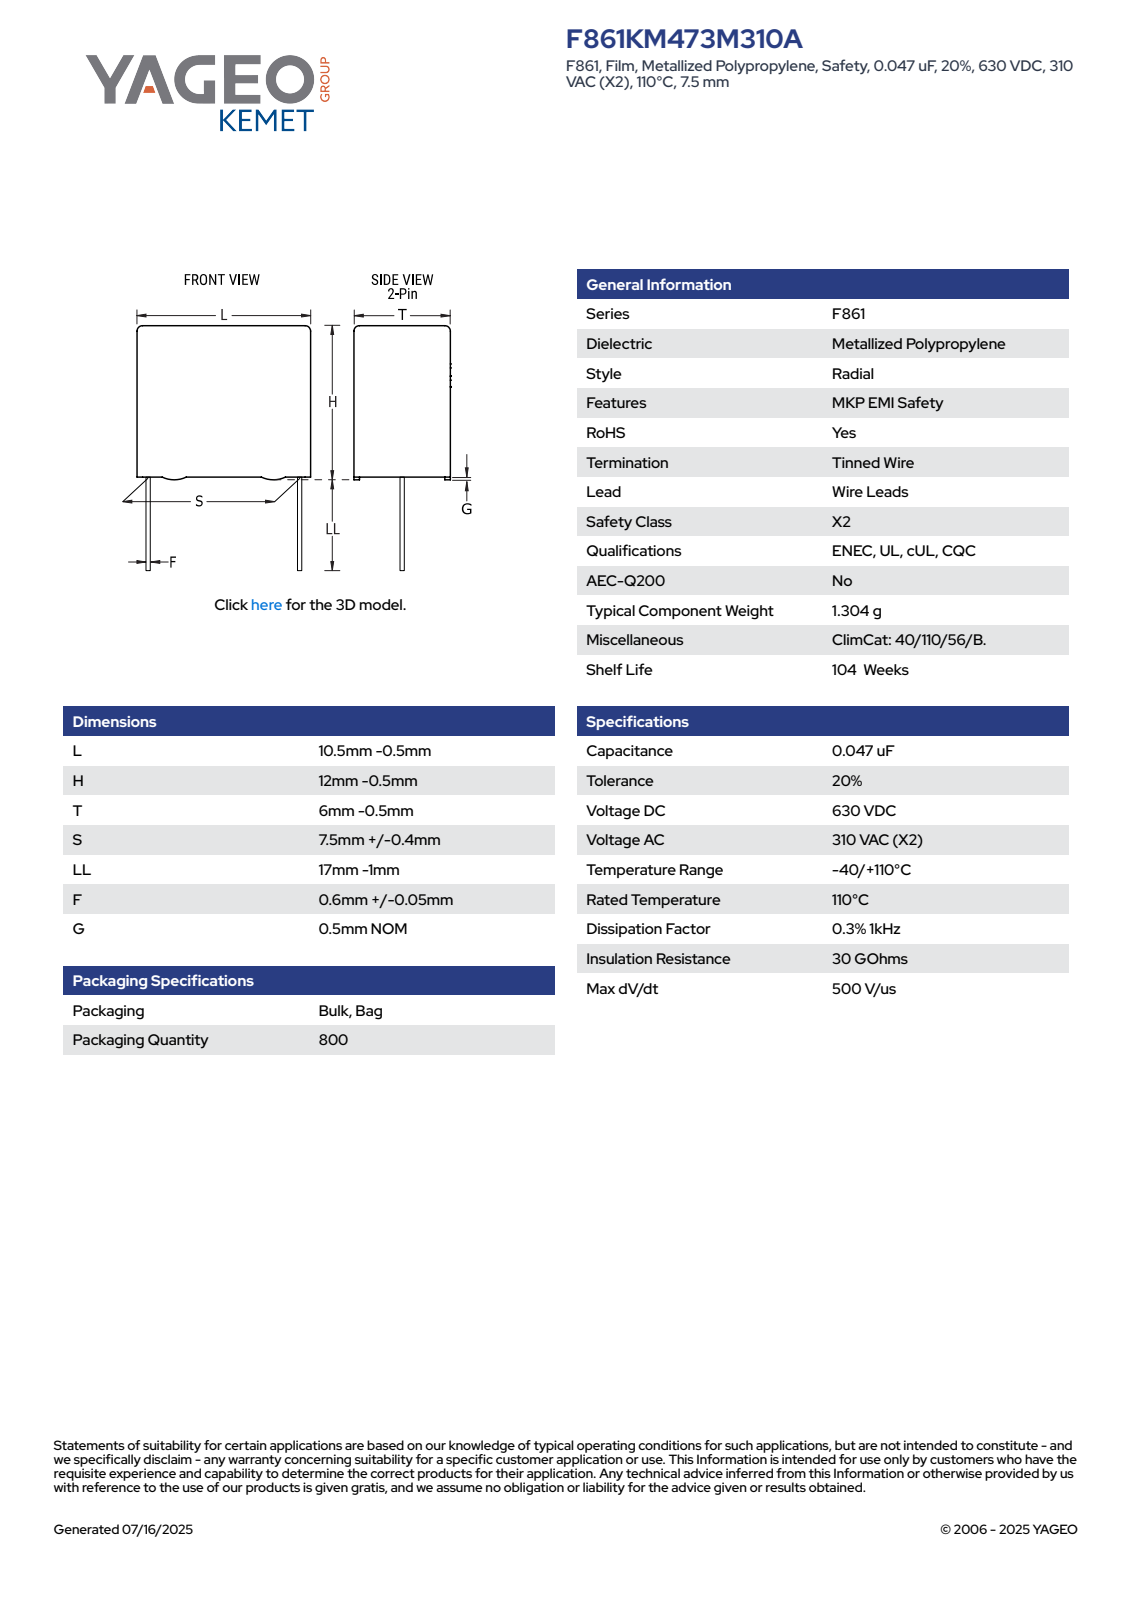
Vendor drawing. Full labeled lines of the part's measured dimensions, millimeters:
Part name (STEP PRODUCT): CFR_RBG_10.5X12X6_L10H11.5T5.5S7.5LL16F0.65G0.5
STEP written by: SolidWorks 2014 (AUTOMOTIVE_DESIGN)
Units: millimetres
Bodies: 4 solids, 89 faces (81 planar, 8 cylindrical, 0 other)
Overall size (bounding box): 27.5 × 10 × 5.5
Volume: 615 mm³ · Surface area: 530 mm²
Round bosses / shafts (diameter × count): ⌀0.65 ×2
Partial cylindrical surfaces — rounded edges, fillets, slot ends (radius × count): R0.5 ×4
Main face-to-face distances: 5.5, 10, 11, 5.19, 0.31, 0.5, 11.5, 4.88, 16, 16.5
